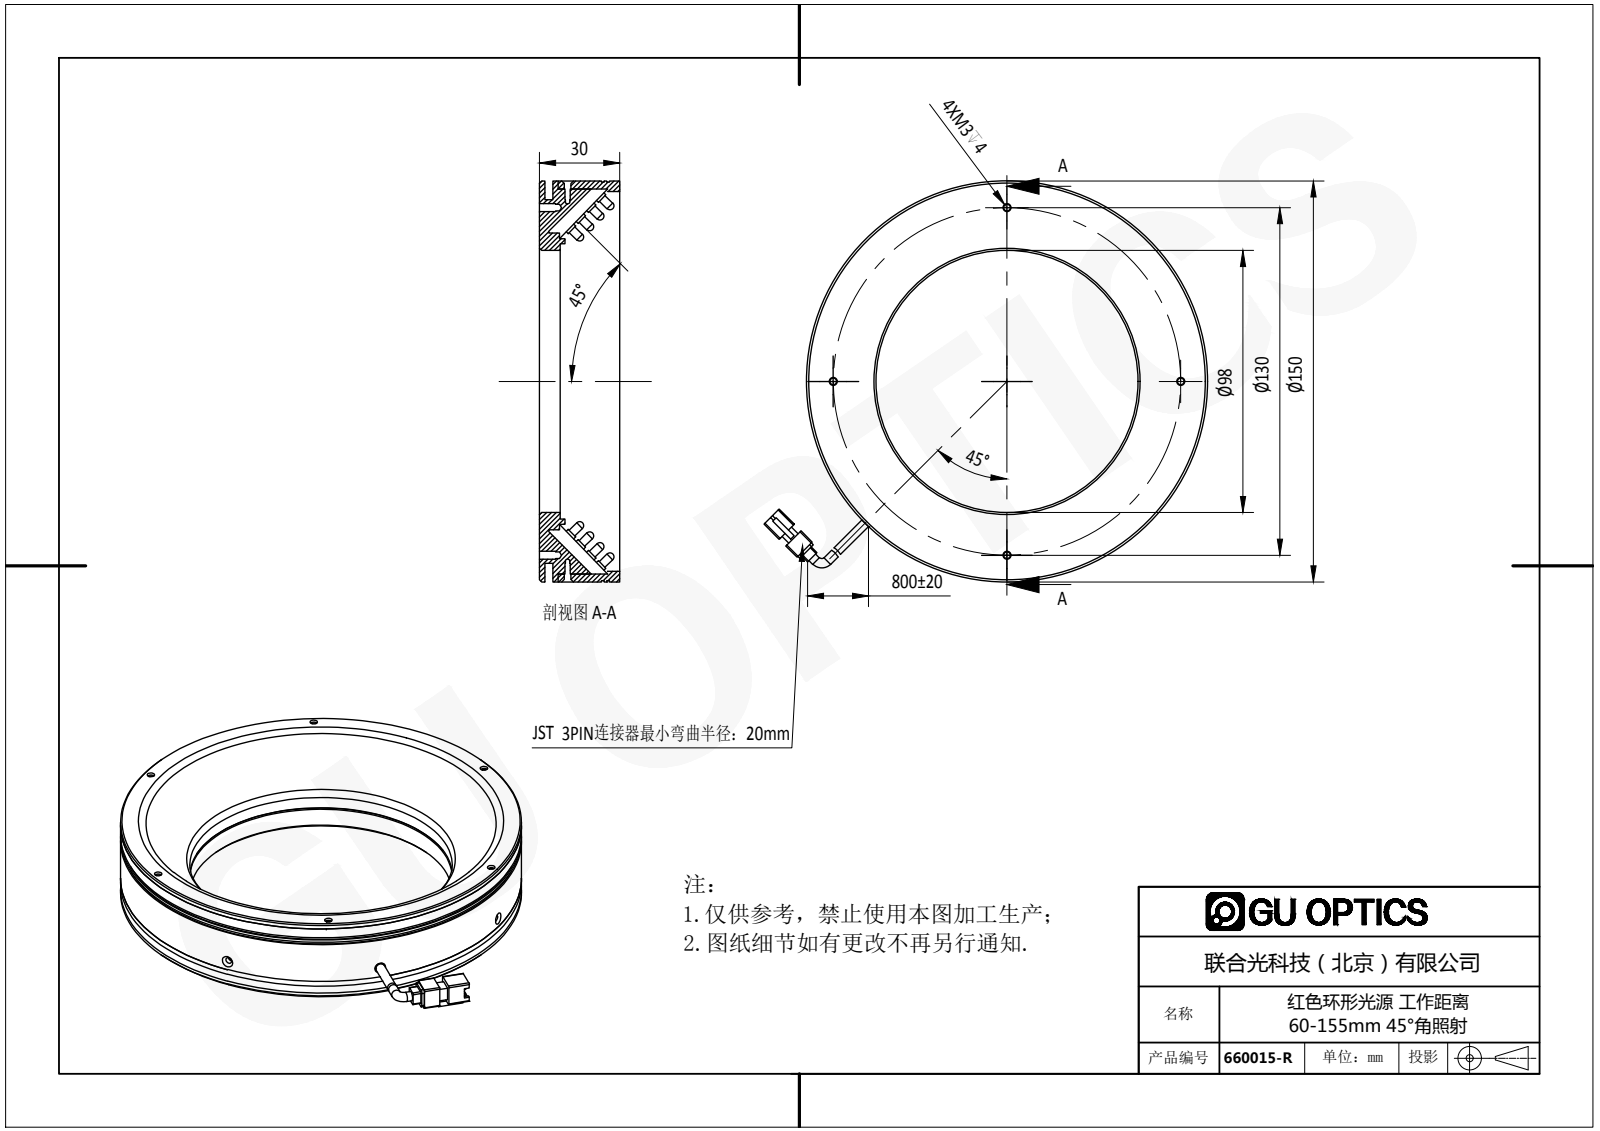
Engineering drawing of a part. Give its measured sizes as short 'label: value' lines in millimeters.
name: 660015-R
written by: SolidWorks 2016 (AUTOMOTIVE_DESIGN)
unit: mm
bodies: 326 solids, 5782 faces (3937 planar, 1453 cylindrical, 392 other)
size: 165.86 × 150 × 32
volume: 171 732 mm³; area: 146 693 mm²
holes: 6× ⌀1.1, 6× ⌀1.4, 6× ⌀1.5, 6× ⌀2.8, 4× ⌀2.5, 4× ⌀3, 4× ⌀3.5, 2× ⌀1.6, 2× ⌀2, 2× ⌀2.4, 1× ⌀3.6, 1× ⌀98
bosses: 320× ⌀3.8, 320× ⌀3, 2× ⌀3.5, 1× ⌀150, 1× ⌀149, 1× ⌀144, 1× ⌀136, 1× ⌀111
rounds: 12× R0.5, 4× R1, 1× R8
face distances: 2, 30, 5, 25, 3, 7, 28, 23, 0.5, 32
hole spacings: 72, 124.71, 18.79, 133.04, 36.1, 52.82, 55.11, 65
